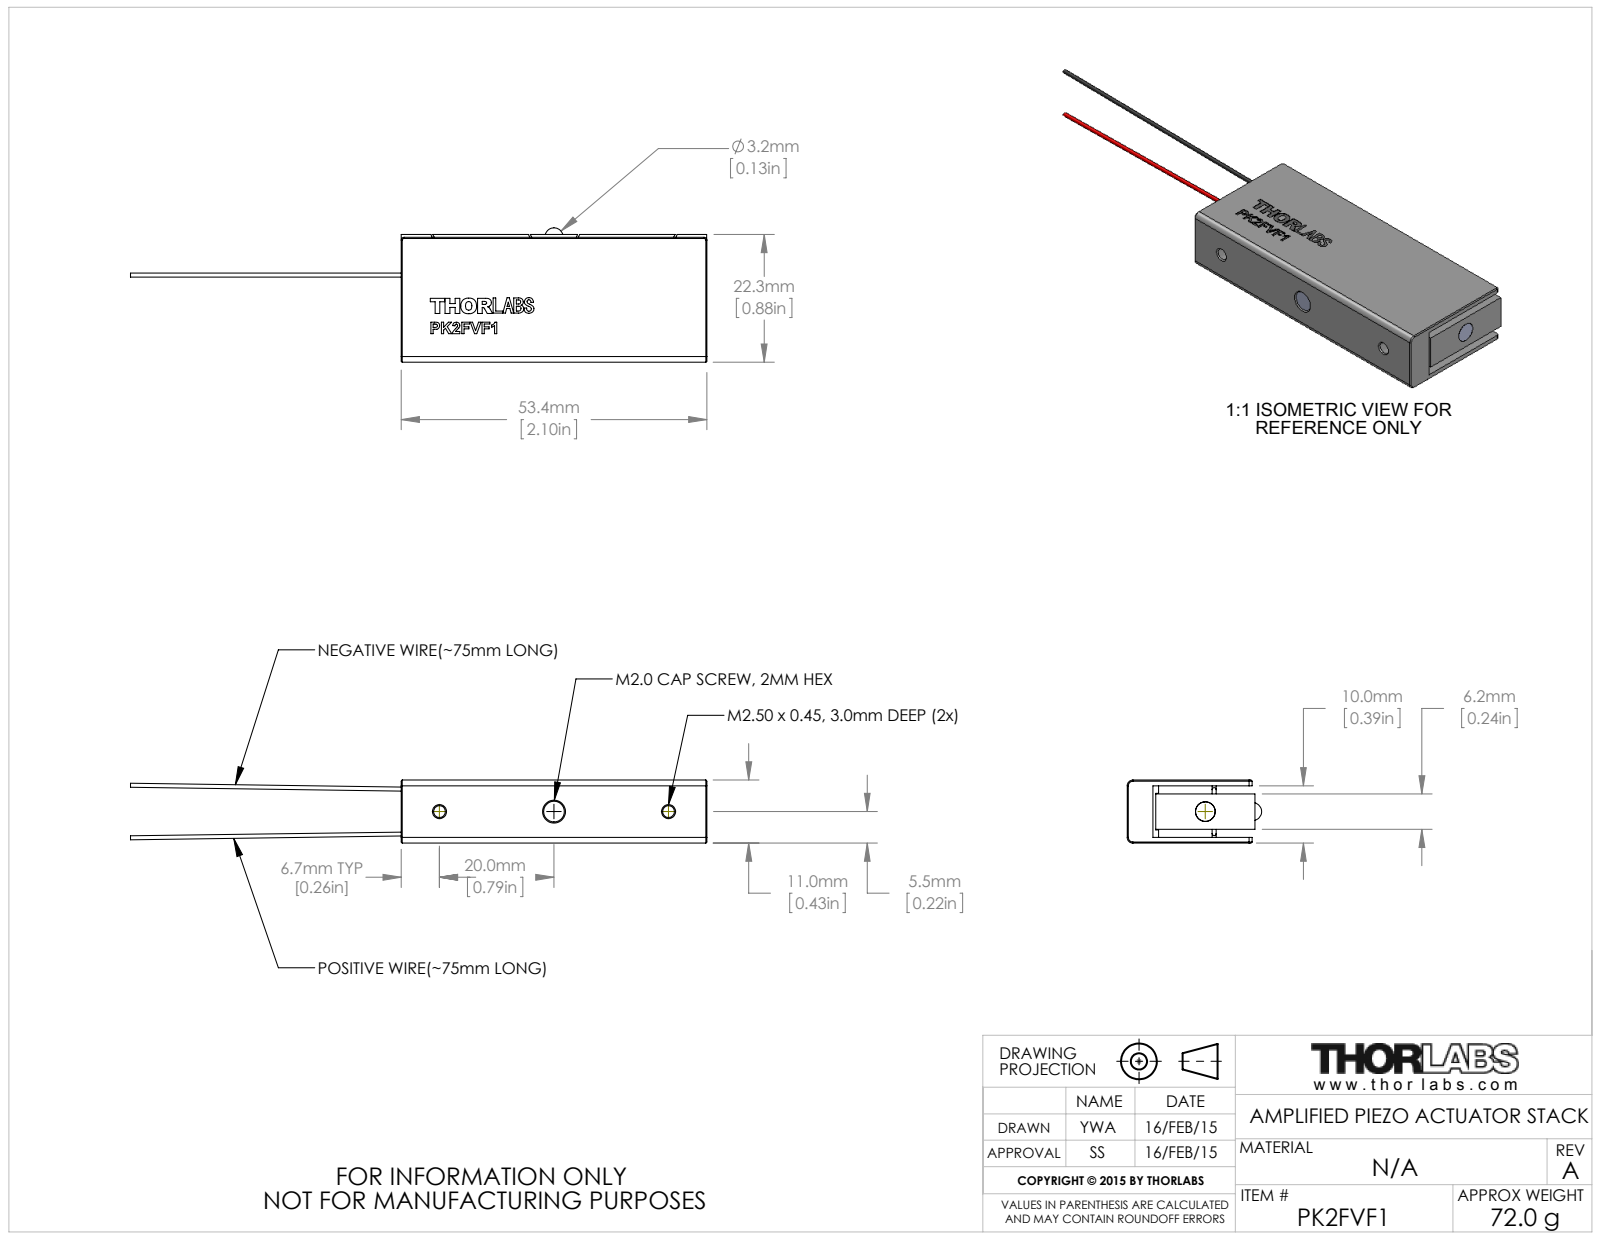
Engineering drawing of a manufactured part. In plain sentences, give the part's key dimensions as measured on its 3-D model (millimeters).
The part is named "screw2; END CUP; screwupdated; PK2FVP2 (+7 more)". Its 3-D file was written by "SolidWorks 2014 (AUTOMOTIVE_DESIGN)". It is 35 solids with 749 faces: 386 planar, 240 cylindrical and 123 other. Overall it measures 100.67 by 23.47 by 11 millimeters. Its volume is 9 131 cubic millimeters and its surface area 11 373 square millimeters. Round holes: 2 of diameter 2.05, 1 of diameter 1.78, 1 of diameter 2.4, 1 of diameter 3.45, 1 of diameter 3.56, 1 of diameter 4. Round bosses or shafts: 16 of diameter 1.2, 2 of diameter 0.7, 1 of diameter 5, 1 of diameter 4.11, 1 of diameter 3.6, 1 of diameter 3.4, 1 of diameter 1.4. Partial cylindrical surfaces (rounded edges, fillets, slot ends): 48 of radius 0.15, 4 of radius 1.57, 2 of radius 0.5, 2 of radius 1. The main face-to-face distances are 10, 1, 8.58, 2.42, 1.42, 7.58, 11, 9, 5, 2.4. The hole center spacings are 20, 40.
